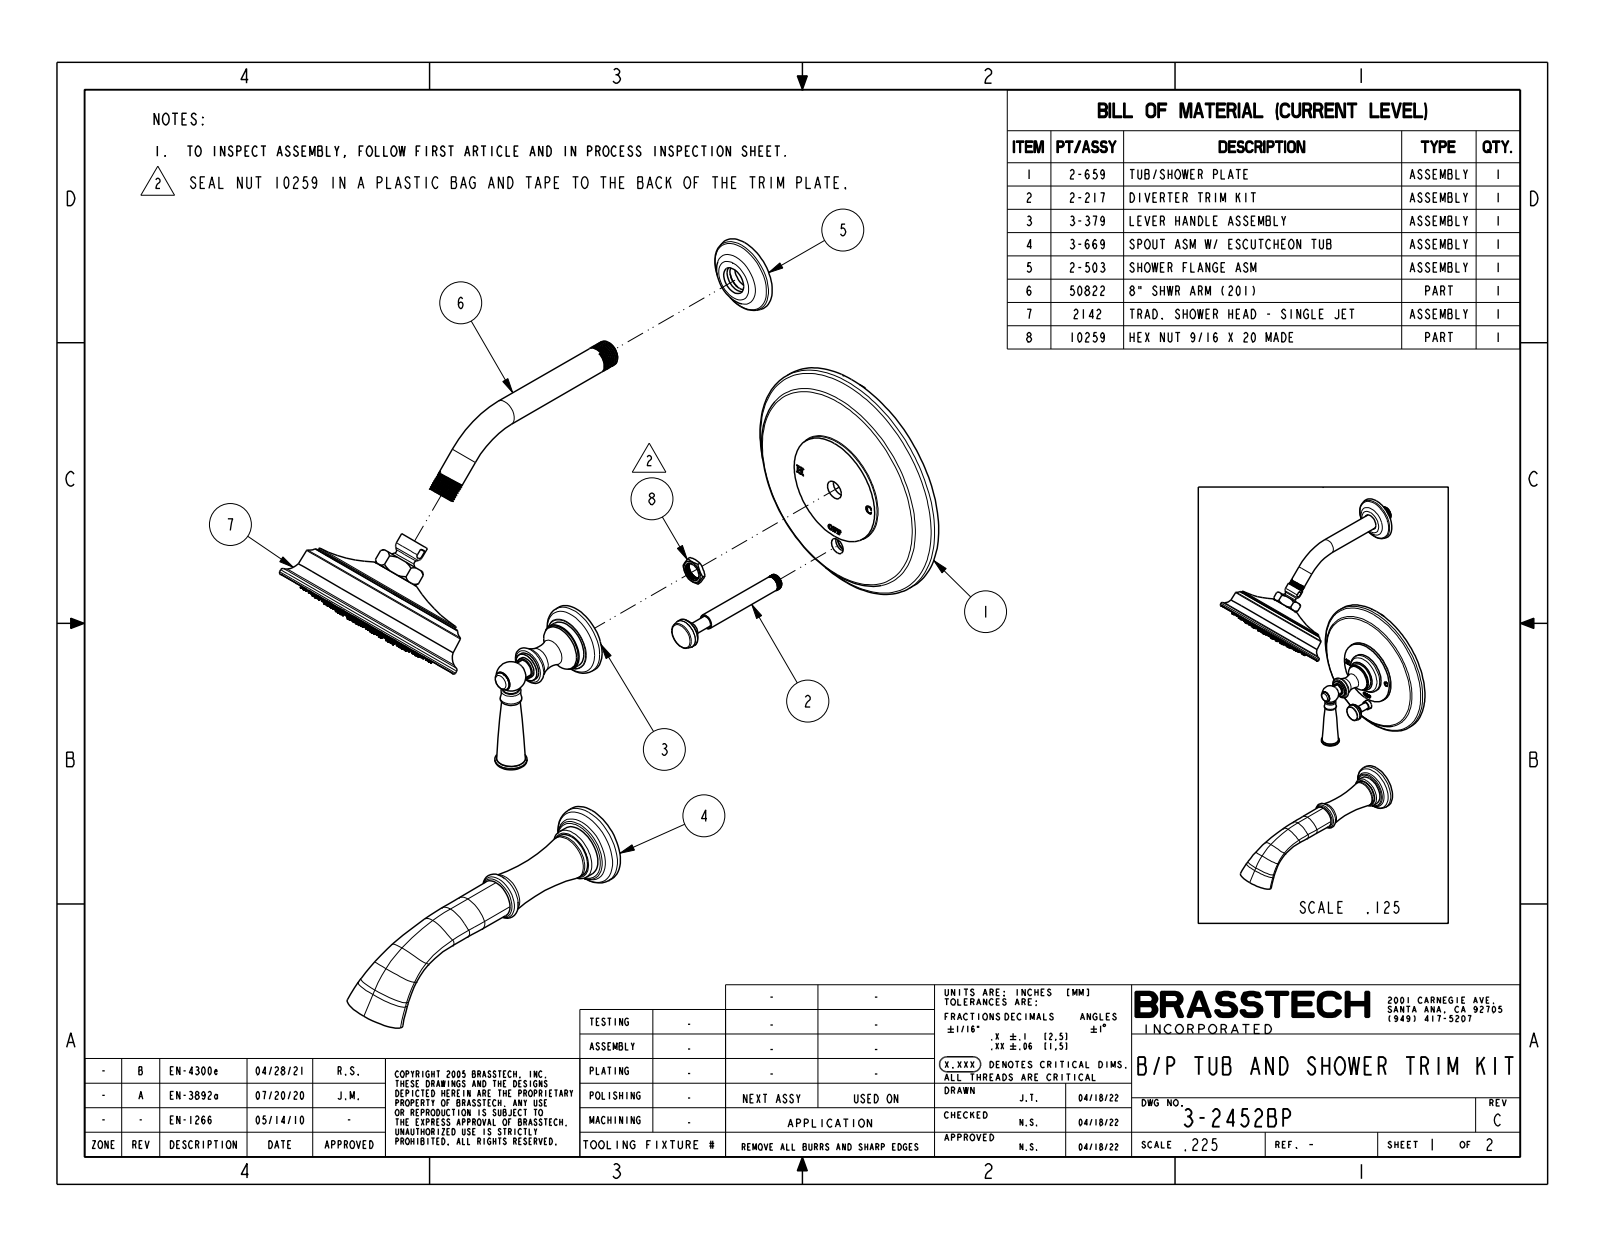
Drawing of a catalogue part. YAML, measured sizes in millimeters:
part_name: "3-2452BP"
step_written_by: "CREO PARAMETRIC BY PTC INC, 2018400 (CONFIG_CONTROL_DESIGN)"
units: millimeters
bodies: {solids: 3, faces: 1312, planar: 280, cylindrical: 246, other: 786}
overall_size: [532.7, 271.6, 190.5]
volume: 1377000
surface_area: 184900
round_holes:
  - {diameter: 1.3, count: 90}
  - {diameter: 5.6, count: 1}
  - {diameter: 15.3, count: 1}
  - {diameter: 134, count: 1}
round_bosses_or_shafts:
  - {diameter: 36.1, count: 2}
  - {diameter: 22.9, count: 2}
  - {diameter: 20.7, count: 2}
  - {diameter: 190.5, count: 1}
  - {diameter: 157.5, count: 1}
  - {diameter: 132.6, count: 1}
  - {diameter: 122.7, count: 1}
  - {diameter: 63, count: 1}
face_to_face_distances: [15.9, 19.1, 3.2, 12.2, 3.7, 6.9, 25.8, 14, 1.8, 1.9]
hole_center_spacings: [57.7, 12.2, 46.7, 24.2, 46.7, 35.8, 56.9, 66.1]
